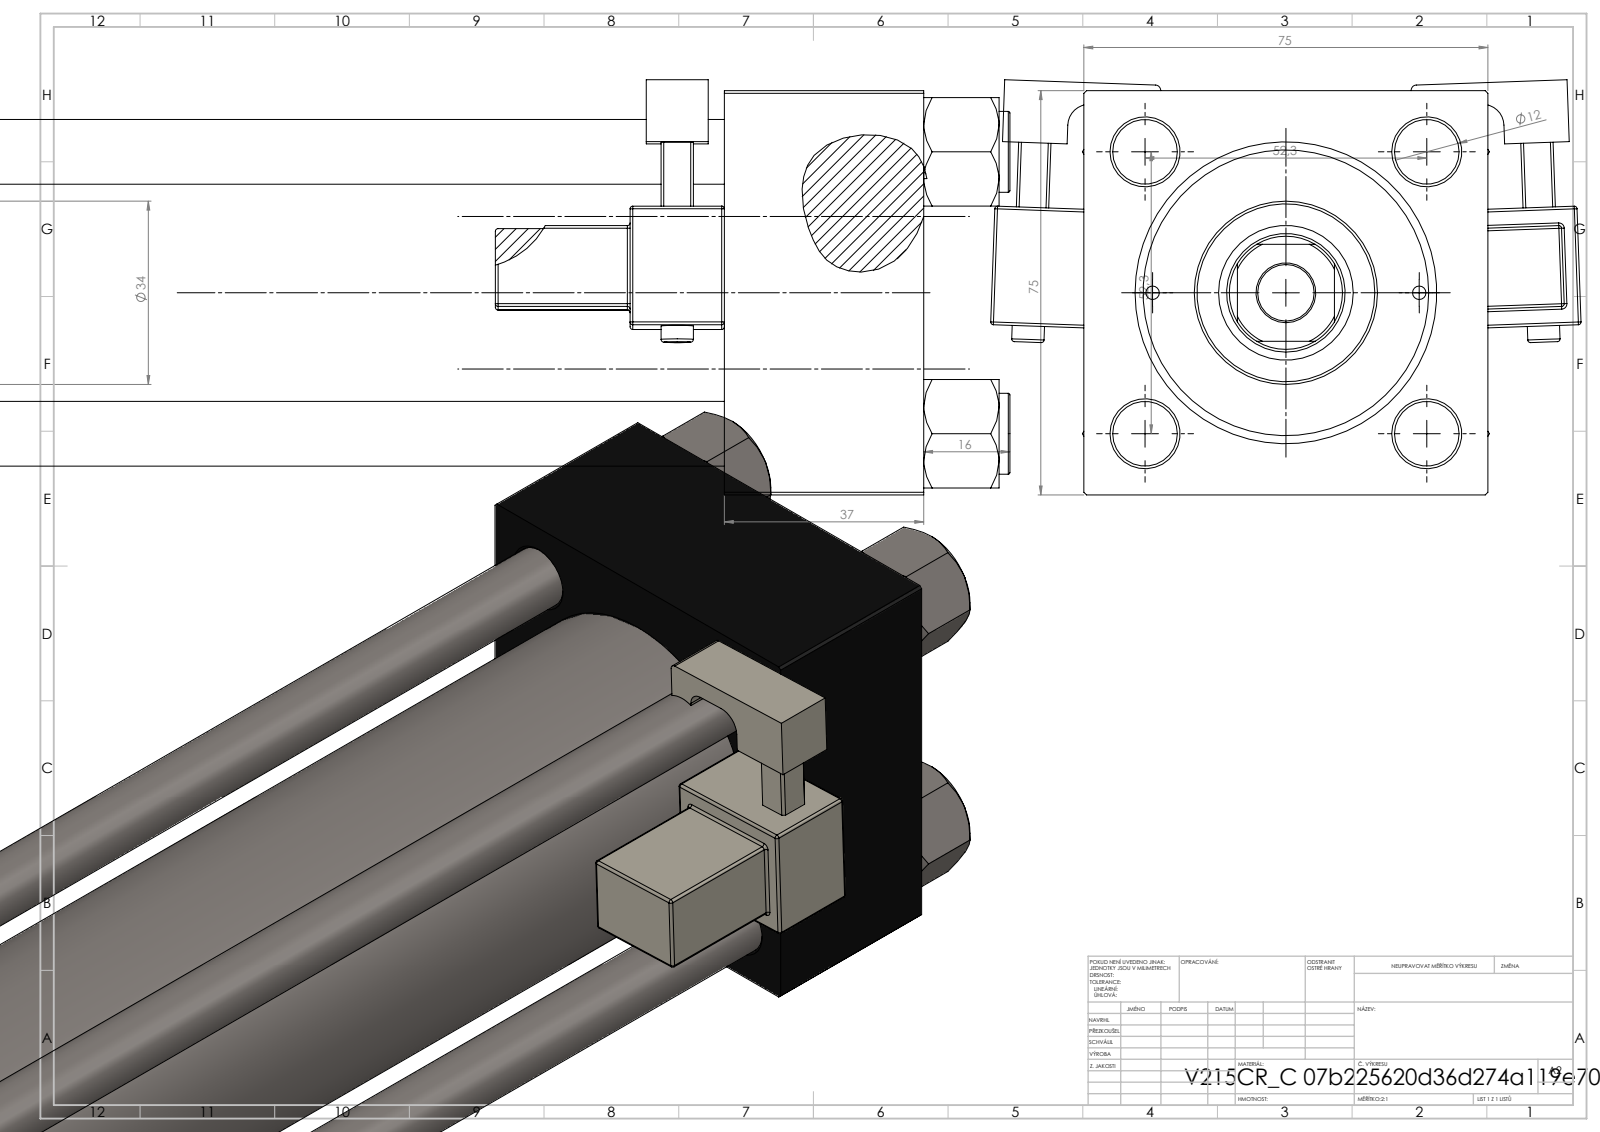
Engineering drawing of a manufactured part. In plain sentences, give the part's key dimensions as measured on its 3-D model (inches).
The part is named "V215_VC_A; V215CR_C_TYCINKA; V215CR_MSU; V215CR_VCP_C (+2 more)". Its 3-D file was written by "SolidWorks 2019 (CONFIG_CONTROL_DESIGN)". It is 13 solids with 1308 faces: 586 planar, 150 cylindrical and 572 other. Overall it measures 18.701 by 4.314 by 3.033 inches. Its volume is 65.36 cubic inches and its surface area 487.4 square inches. Round holes: 4 of diameter 0.472, 2 of diameter 0.098, 2 of diameter 0.276, 2 of diameter 0.825, 2 of diameter 1.181, 1 of diameter 0.413, 1 of diameter 0.866, 1 of diameter 0.984, 1 of diameter 1.614, 1 of diameter 1.969, 1 of diameter 2.087. Round bosses or shafts: 4 of diameter 0.591, 2 of diameter 0.236, 1 of diameter 2.205, 1 of diameter 1.339. Partial cylindrical surfaces (rounded edges, fillets, slot ends): 48 of radius 0.02, 2 of radius 0.039, 2 of radius 0.098, 2 of radius 0.157, 1 of radius 0.413. The main face-to-face distances are 2.953, 1.457, 17.087, 15.63, 14.764, 13.307, 2.323, 15.957, 14.5, 1.193. The hole center spacings are 1.031, 1.456, 2.059, 2.253, 0.974, 2.912, 1.949, 14.705.
